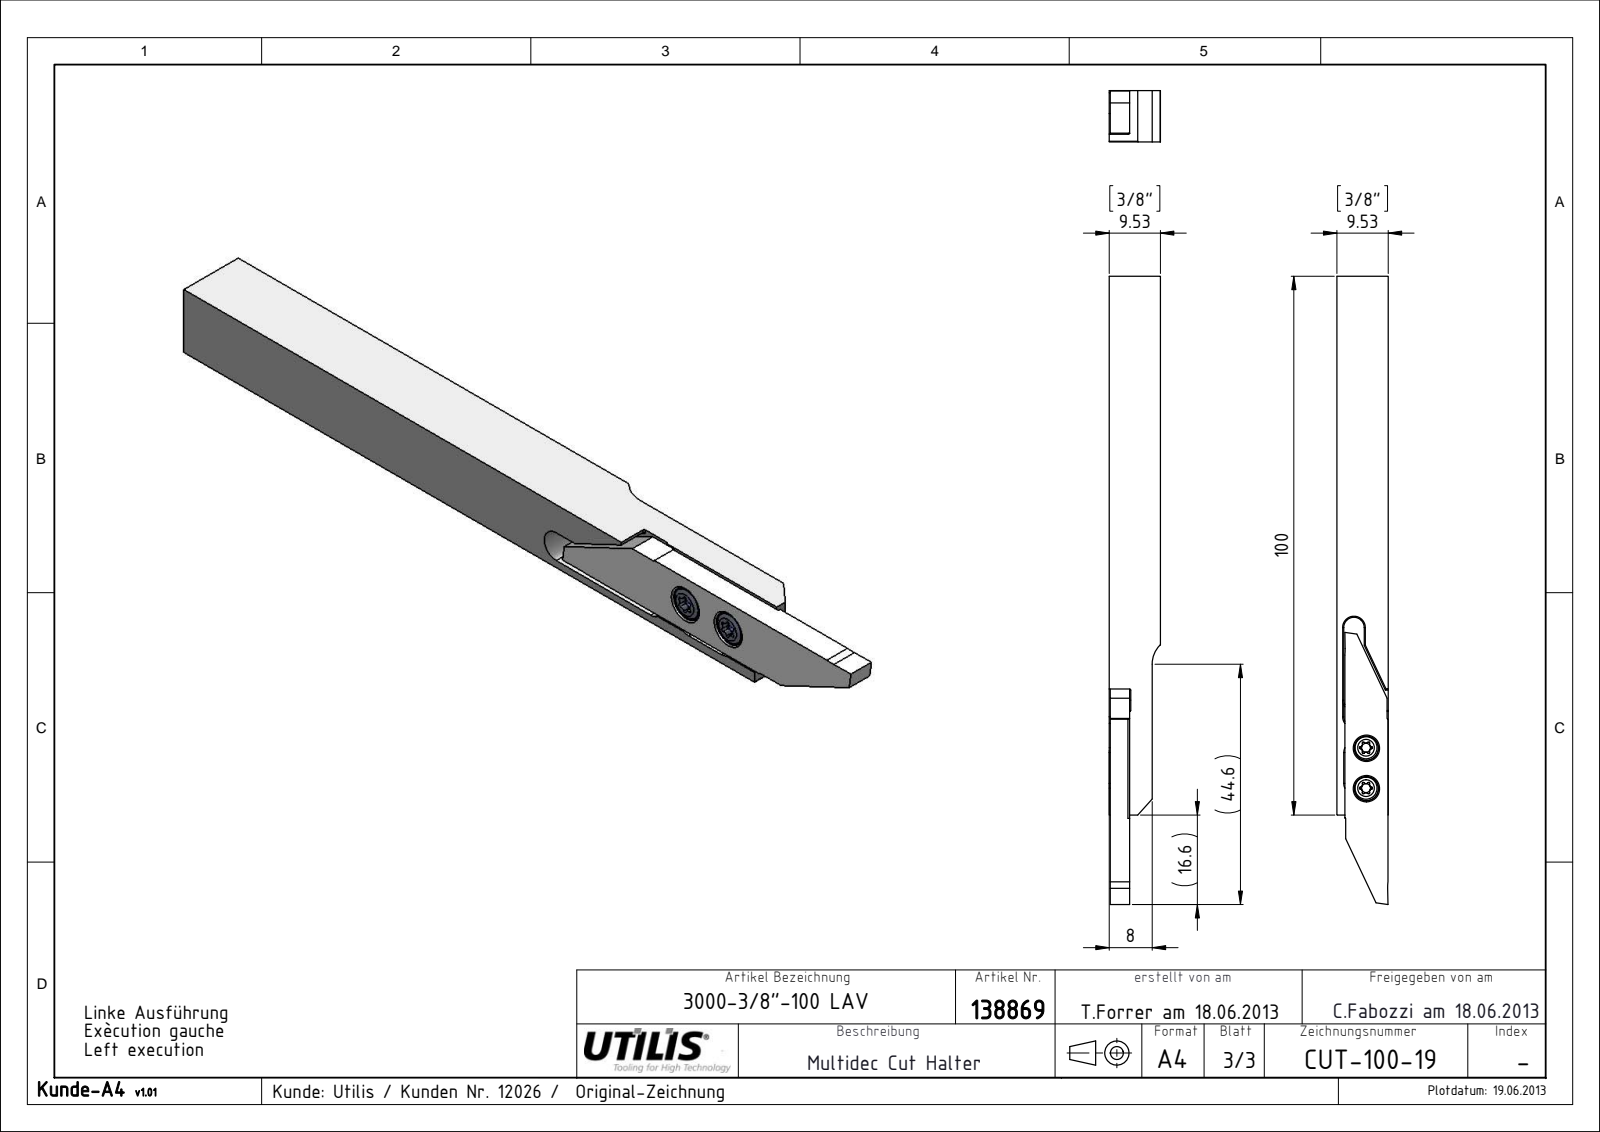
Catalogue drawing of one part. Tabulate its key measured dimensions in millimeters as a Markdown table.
| quantity | value |
| --- | --- |
| part name | CUT-100-Kunde_3000-3-8-100 LAV; CUT- 3000 R+L Lang NUR FÜR KUNDEN _L-Lang; MSP-16_M3x7.3 T08; CUT-100-19 |
| STEP written by | SolidWorks 2014 (CONFIG_CONTROL_DESIGN) |
| units | millimeters |
| bodies | 4 solids, 118 faces (34 planar, 56 cylindrical, 28 other) |
| overall size | 116.6 × 9.53 × 9.53 |
| volume | 8 707 mm³ |
| surface area | 5 272 mm² |
| round holes (diameter × count) | 2.5 × 2, 4.9 × 2 |
| round bosses / shafts (diameter × count) | 4.1 × 2, 3 × 2 |
| partial cylindrical surfaces (radius × count) | 0.2 × 12, 0.45 × 12, 2.1 × 4, 10 × 2, 5 × 1 |
| main face-to-face distances | 9.52, 9.53, 3.8, 5.73, 8, 3.6, 9.33, 4.2, 7.8, 1.53 |
| hole center spacings | 3.75, 7.5, 3.65, 3.85, 7.4, 7.6 |
